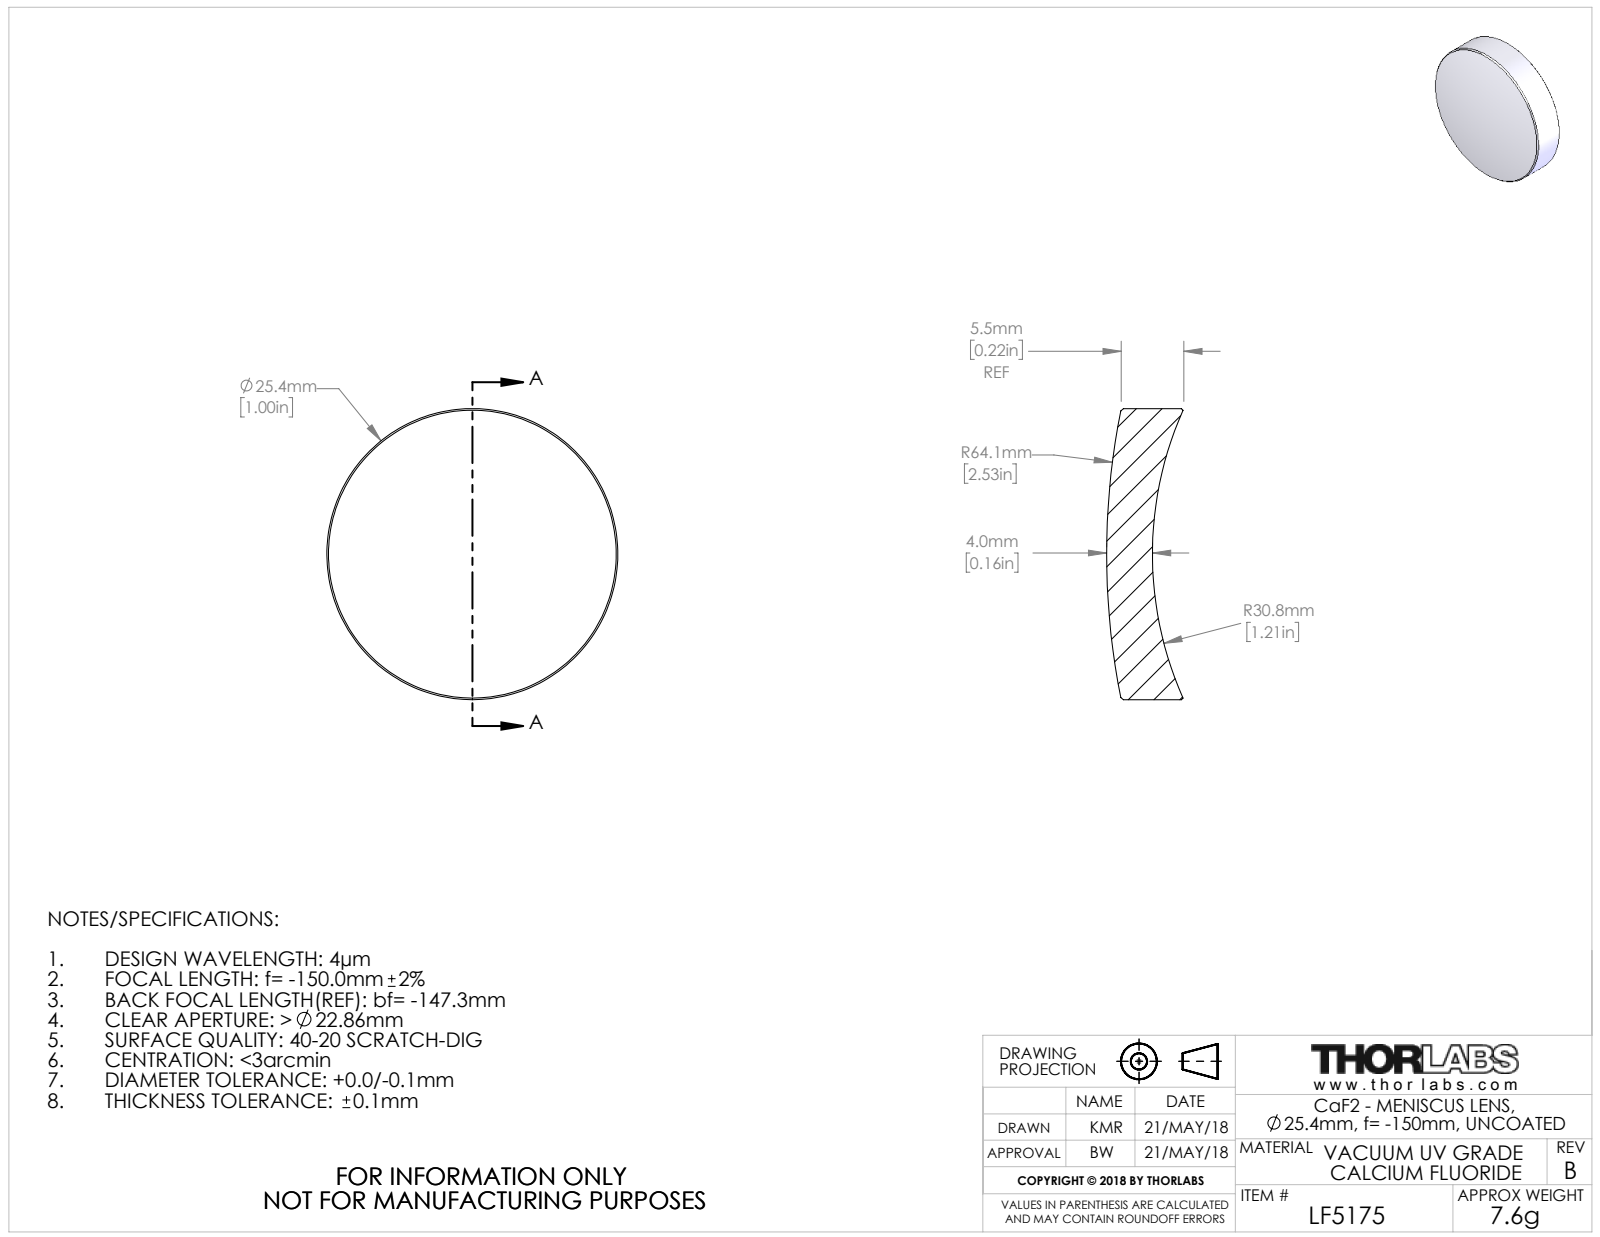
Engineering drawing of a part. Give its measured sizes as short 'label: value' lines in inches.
name: 22002-E0W
written by: SolidWorks 2016 (CONFIG_CONTROL_DESIGN)
unit: in
bodies: 1 solid, 10 faces (0 planar, 2 cylindrical, 8 other)
size: 1 × 1 × 0.263
volume: 0.146 in³; area: 2.26 in²
bosses: 1× ⌀1
